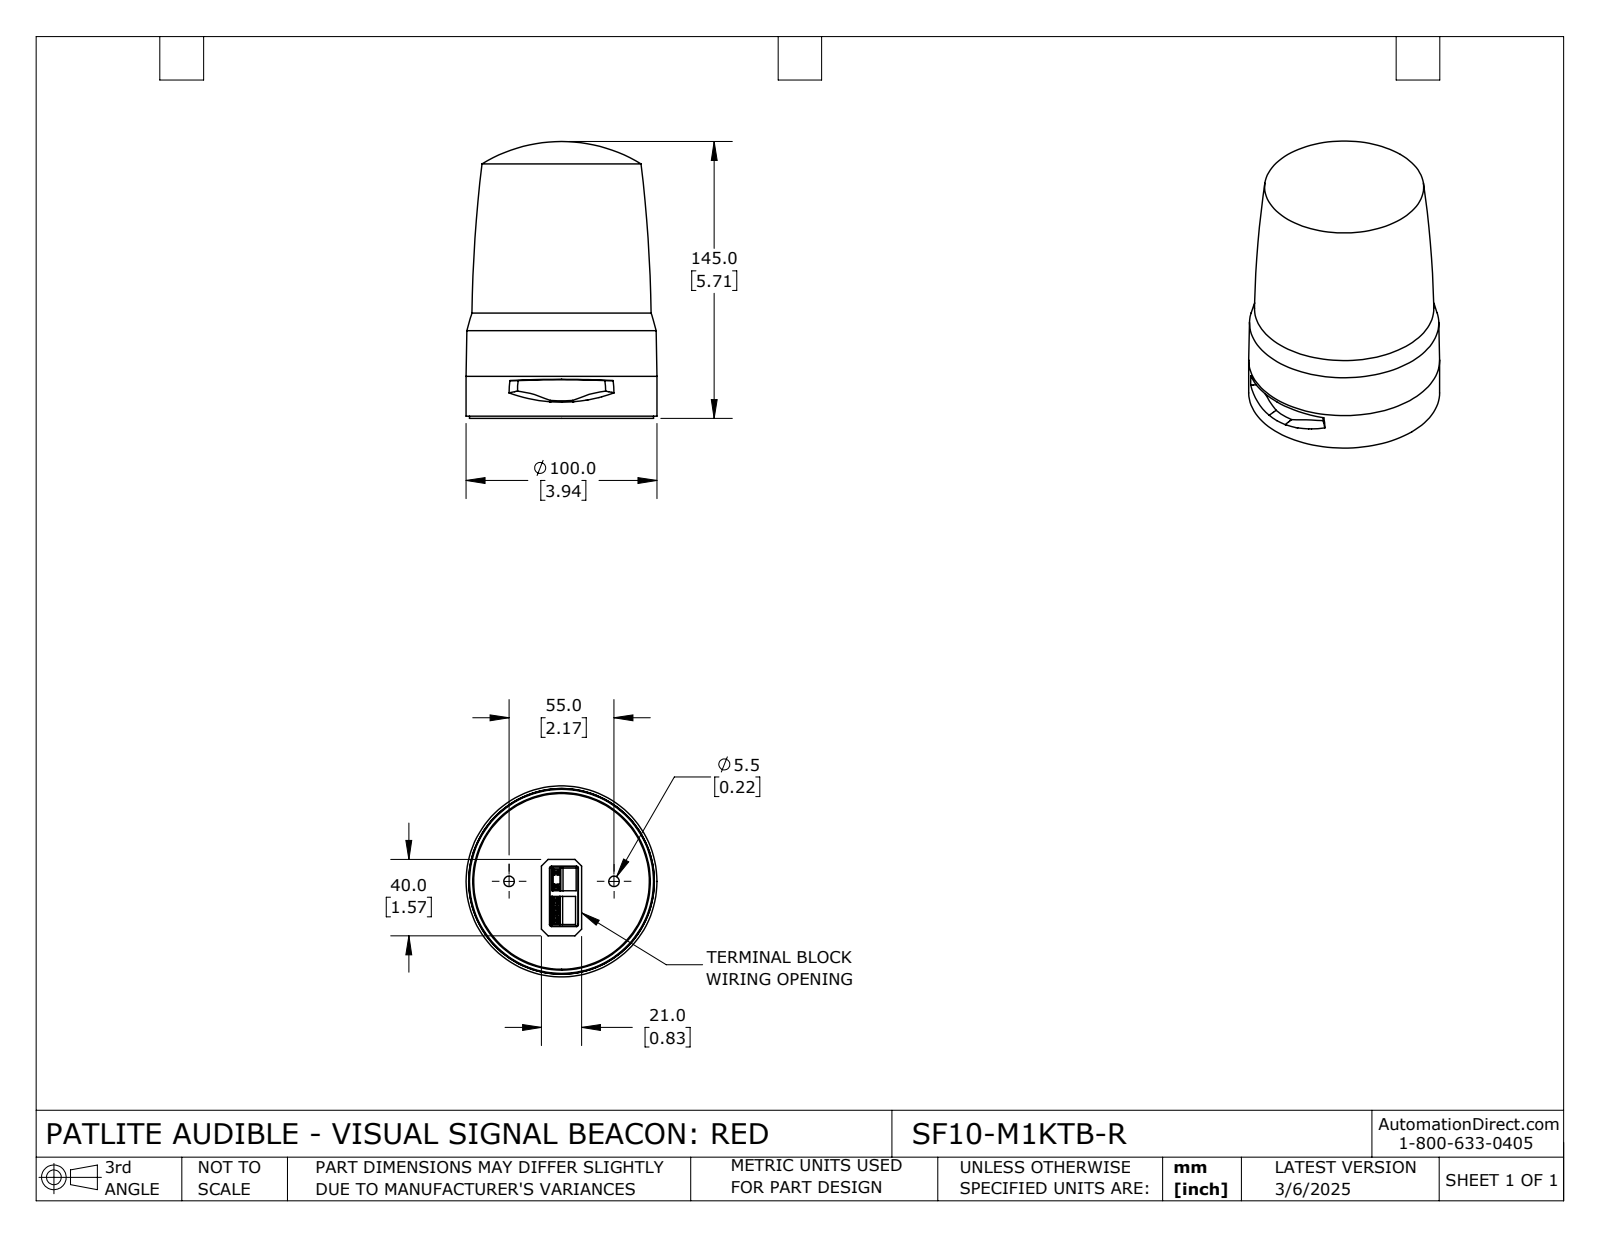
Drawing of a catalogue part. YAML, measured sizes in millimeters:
part_name: "SF10-M1KTB-R"
step_written_by: "SolidWorks 2024 (CONFIG_CONTROL_DESIGN)"
units: millimeters
bodies: {solids: 2, faces: 275, planar: 174, cylindrical: 31, other: 70}
overall_size: [145, 100, 100]
volume: 875277
surface_area: 79857
round_holes:
  - {diameter: 5.5, count: 2}
  - {diameter: 13, count: 2}
  - {diameter: 93, count: 1}
round_bosses_or_shafts:
  - {diameter: 100, count: 1}
  - {diameter: 96.4, count: 1}
  - {diameter: 94.5, count: 1}
  - {diameter: 93.2, count: 1}
  - {diameter: 92, count: 1}
partial_cylinders:
  - {radius: 1, count: 4}
  - {radius: 0.3, count: 2}
  - {radius: 44.75, count: 1}
  - {radius: 45, count: 1}
face_to_face_distances: [6.3, 18.2, 11.9, 5.6, 12.6, 5.1, 0.4, 4.7, 1.2, 17]
hole_center_spacings: [27.5, 55]
